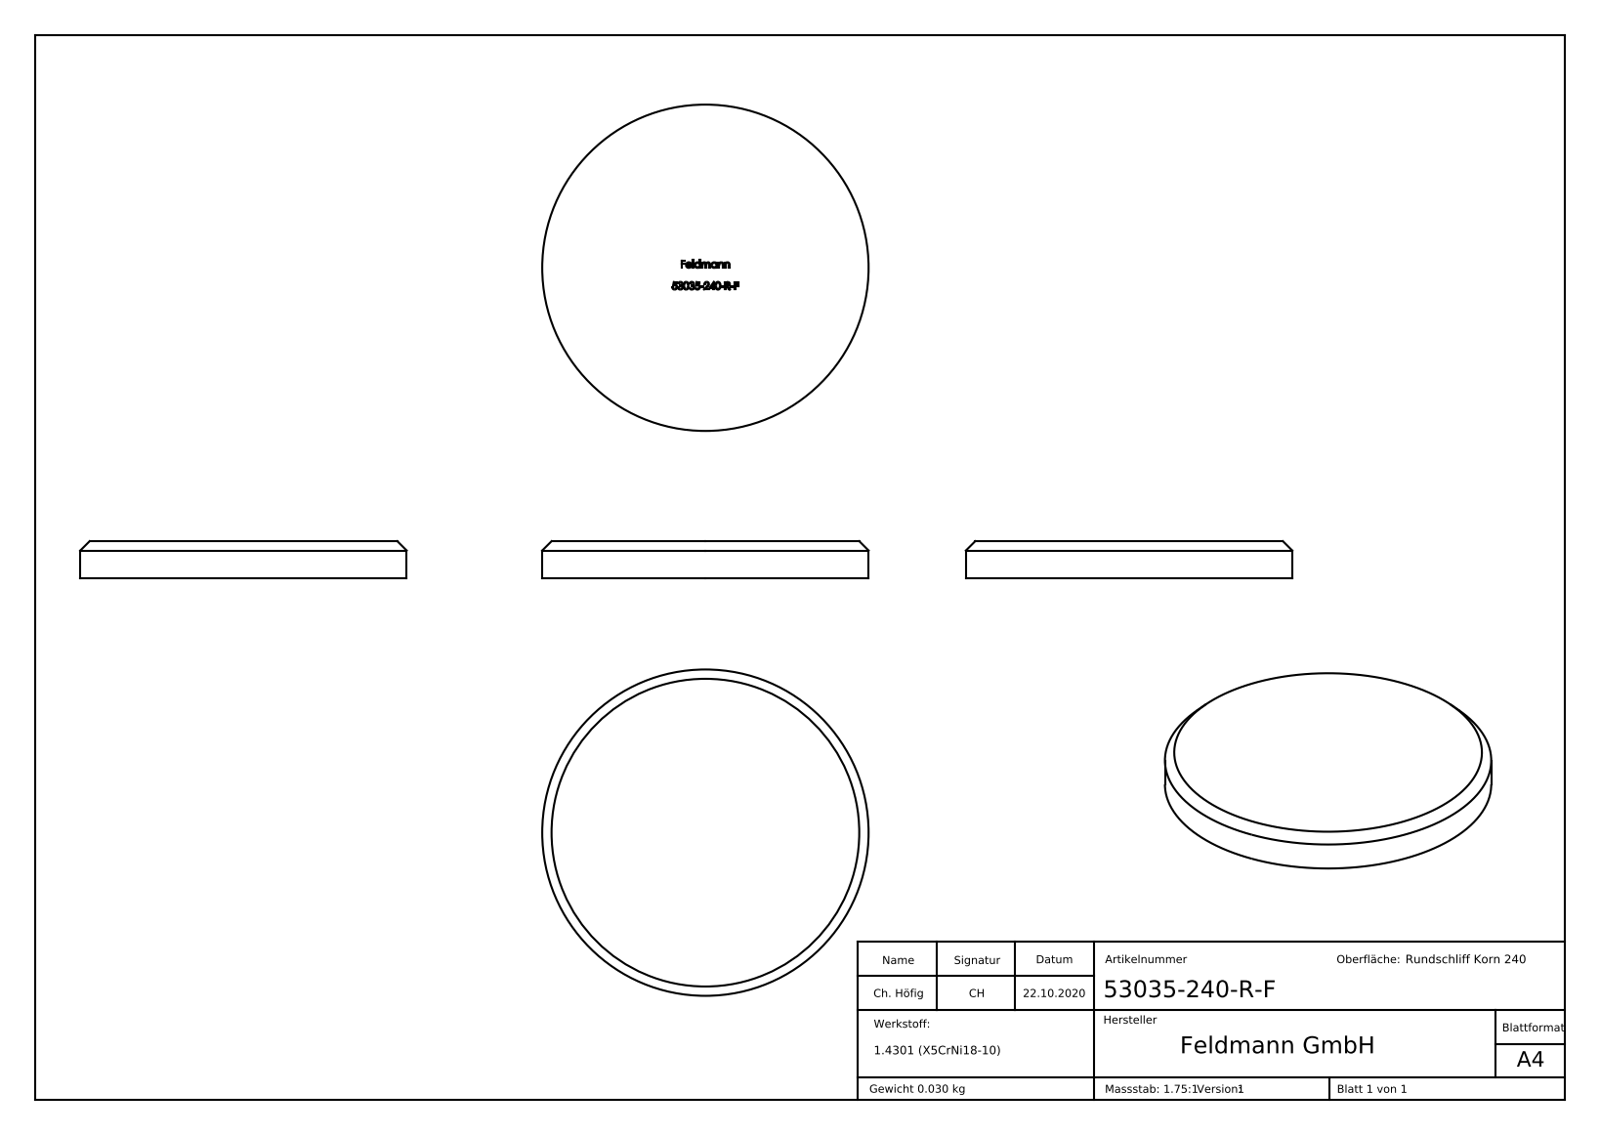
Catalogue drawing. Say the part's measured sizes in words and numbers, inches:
The part is named "53035-240-R-F". Its 3-D file was written by "SolidWorks 2018 (CONFIG_CONTROL_DESIGN)". It is 1 solid with 279 faces: 154 planar, 2 cylindrical and 123 other. Overall it measures 1.378 by 1.378 by 0.157 inches. Its volume is 0.232 cubic inches and its surface area 3.573 square inches. Round bosses or shafts: 1 of diameter 1.378. The main face-to-face distances are 0.157, 0.154, 0.091, 0.048, 0.137, 0.031, 0.07, 0.018, 0.021, 0.087.
